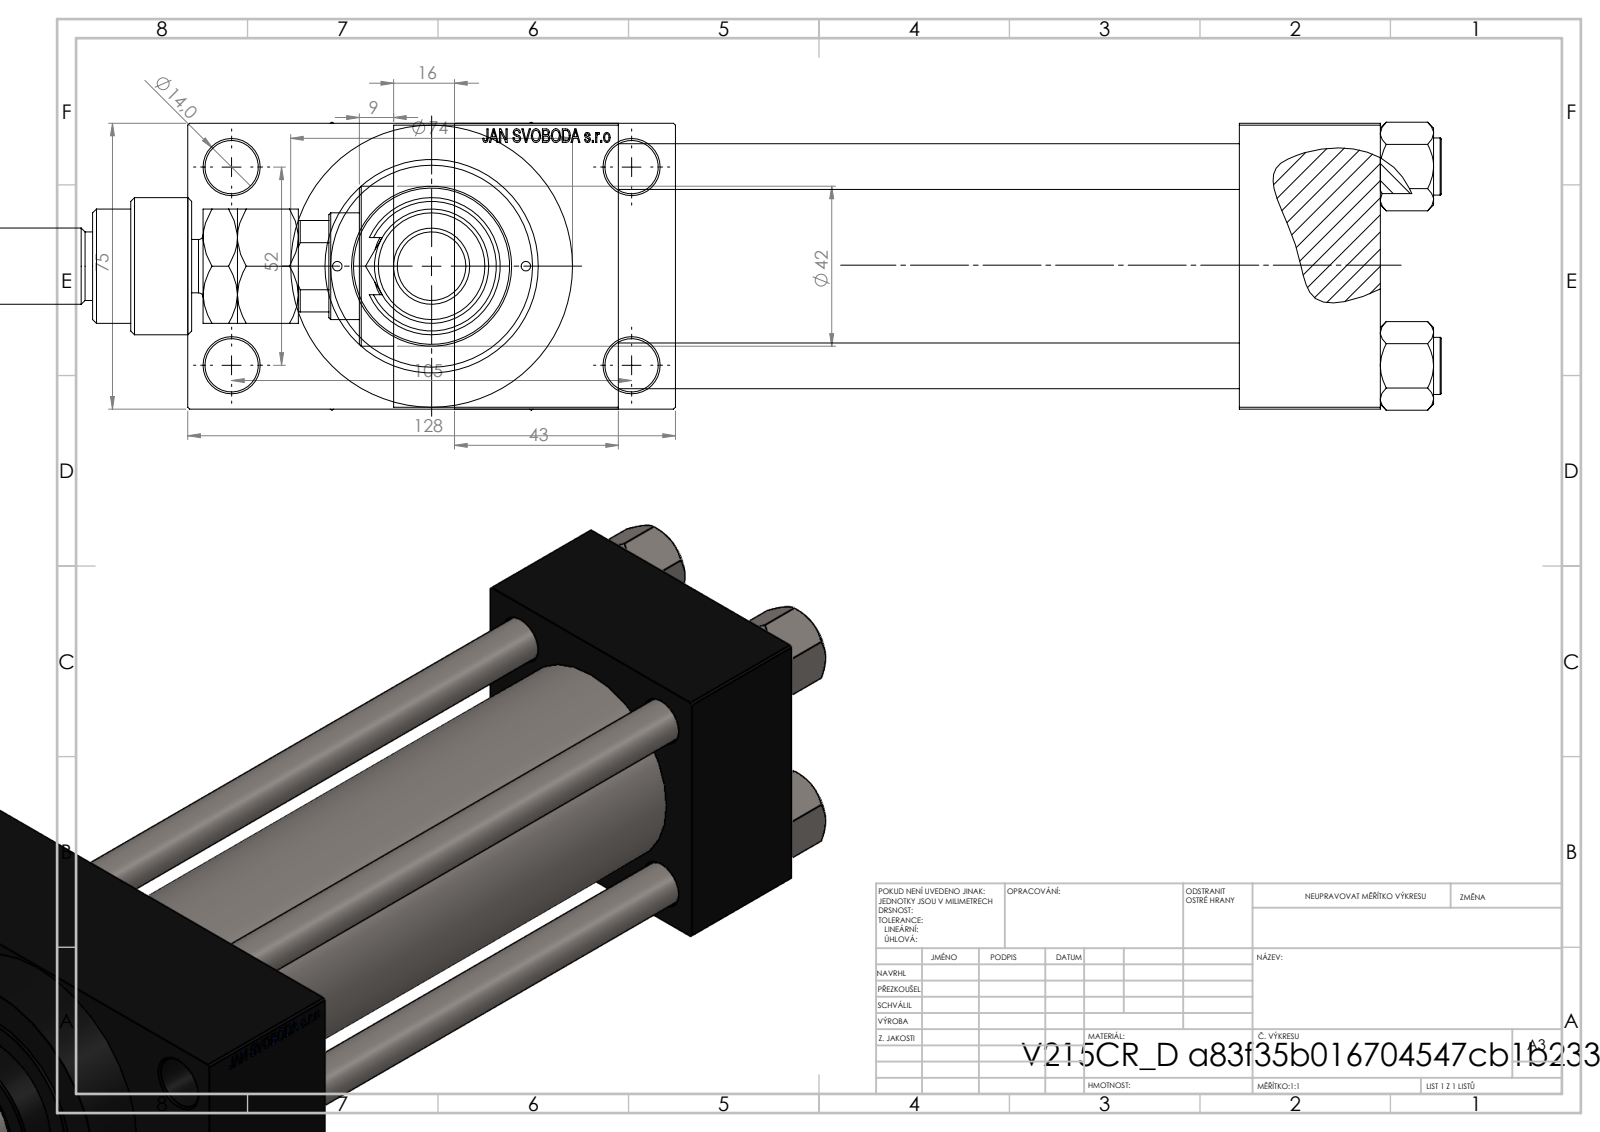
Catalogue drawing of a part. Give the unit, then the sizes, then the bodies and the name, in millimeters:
Units: millimetres
Overall size (bounding box): 384 × 128 × 75.54
Round holes (diameter × count): ⌀12 ×4, ⌀14 ×4, ⌀2.5 ×2, ⌀7 ×2, ⌀20.96 ×2, ⌀30 ×2, ⌀18.5 ×1, ⌀28 ×1, ⌀31 ×1, ⌀41 ×1, ⌀50 ×1, ⌀53 ×1
Round bosses / shafts (diameter × count): ⌀15 ×4, ⌀74 ×1, ⌀56 ×1, ⌀42 ×1, ⌀36 ×1, ⌀30 ×1, ⌀22 ×1, ⌀20 ×1
Partial cylindrical surfaces — rounded edges, fillets, slot ends (radius × count): R7.5 ×1, R12 ×1, R13.5 ×1
Main face-to-face distances: 75, 163, 37, 200, 26.5, 43, 243, 206, 101.5, 16
Hole centre spacings: 26.19, 26.35, 36.98, 38.03, 52.3, 57.22, 58.43, 58.59
Volume: 1 019 000 mm³ · Surface area: 243 822 mm²
Bodies: 13 solids, 1196 faces (527 planar, 105 cylindrical, 564 other)
Part name (STEP PRODUCT): MFA; NUT_M5_D; V215CR_D_TYCINKA; V215_VC_A (+3 more)
STEP written by: SolidWorks 2019 (CONFIG_CONTROL_DESIGN)
